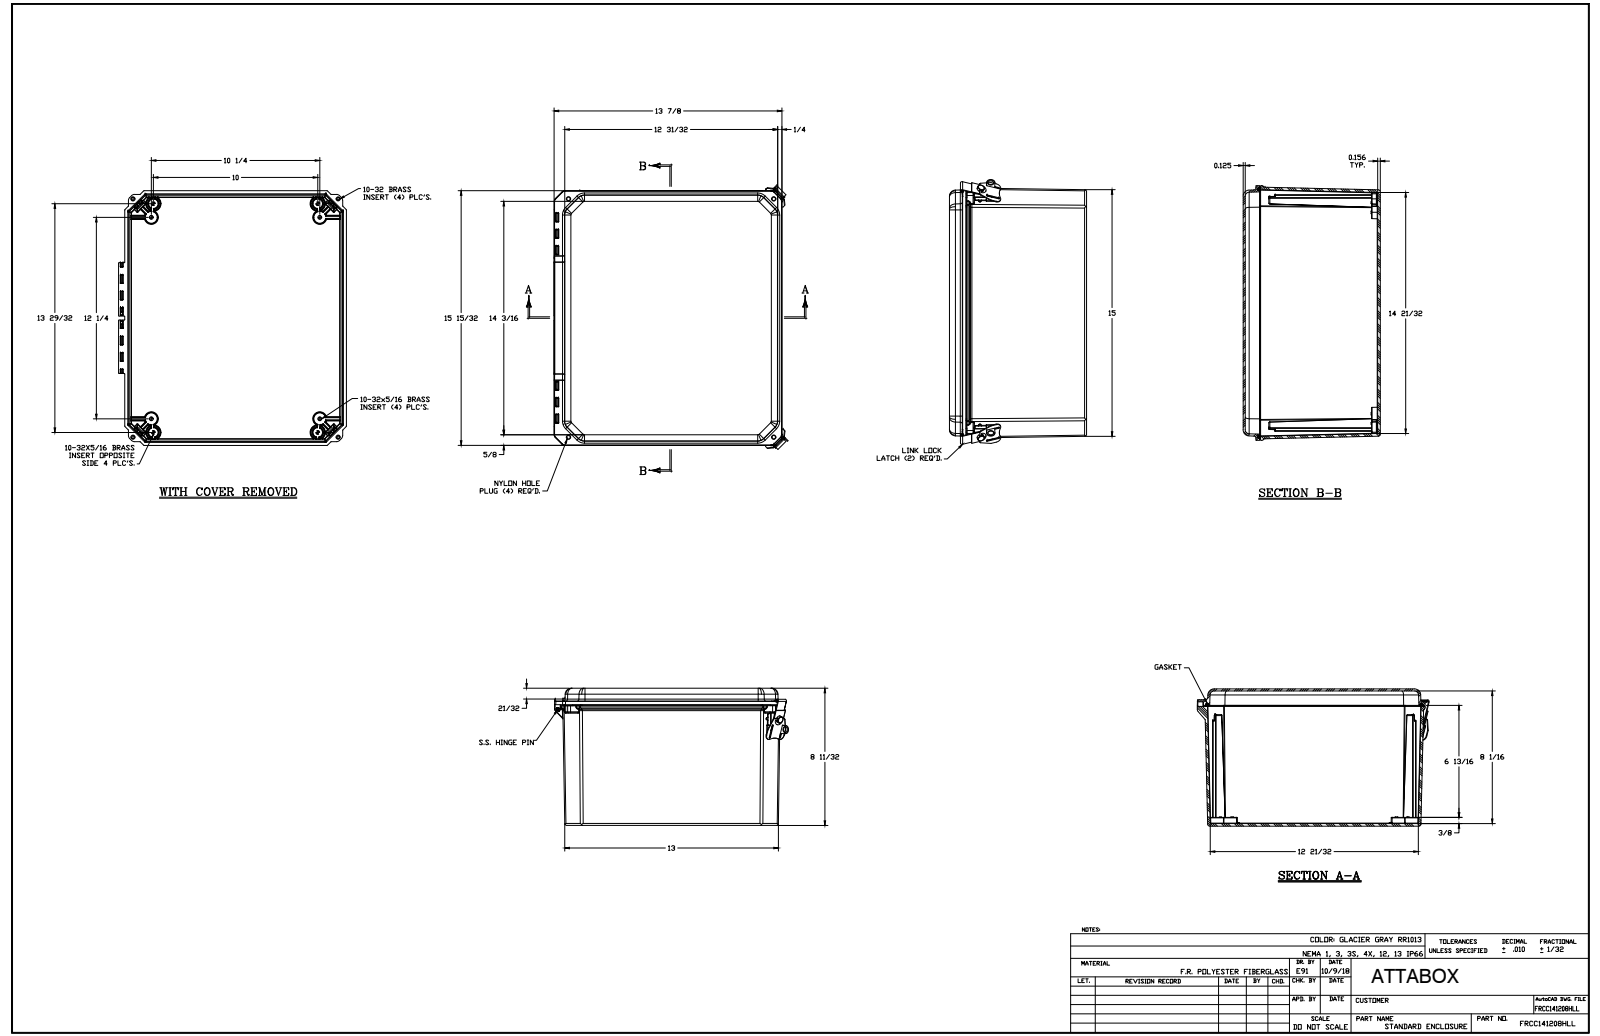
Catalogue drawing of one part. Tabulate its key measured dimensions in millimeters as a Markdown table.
| quantity | value |
| --- | --- |
| part name | FRCC141208HLL |
| STEP written by | SolidWorks 2018 (AUTOMOTIVE_DESIGN) |
| units | millimeters |
| bodies | 33 solids, 2378 faces (713 planar, 936 cylindrical, 729 other) |
| overall size | 417 × 364 × 211.9 |
| volume | 2 206 000 mm³ |
| surface area | 1 173 000 mm² |
| round holes (diameter × count) | 4 × 12, 3.9 × 8, 2.5 × 4, 3.8 × 4, 5.6 × 4, 6.4 × 4, 7.9 × 4, 1.3 × 2, 3 × 2, 9.2 × 2, 3.5 × 1 |
| round bosses / shafts (diameter × count) | 6.2 × 12, 5.3 × 4, 5.1 × 4, 3.4 × 3, 15.2 × 2, 1.3 × 2 |
| partial cylindrical surfaces (radius × count) | 0.3 × 222, 0.1 × 116, 0.5 × 59, 3.2 × 41, 0.8 × 38, 1 × 28, 6.4 × 26, 0.8 × 24 |
| main face-to-face distances | 3.2, 4, 208.7, 204.8, 211.9, 207.9, 4.1, 4, 186.5, 25.4 |
| hole center spacings | 40.2, 445.8, 459.8, 10.9, 20.1, 21, 32.5, 258 |
